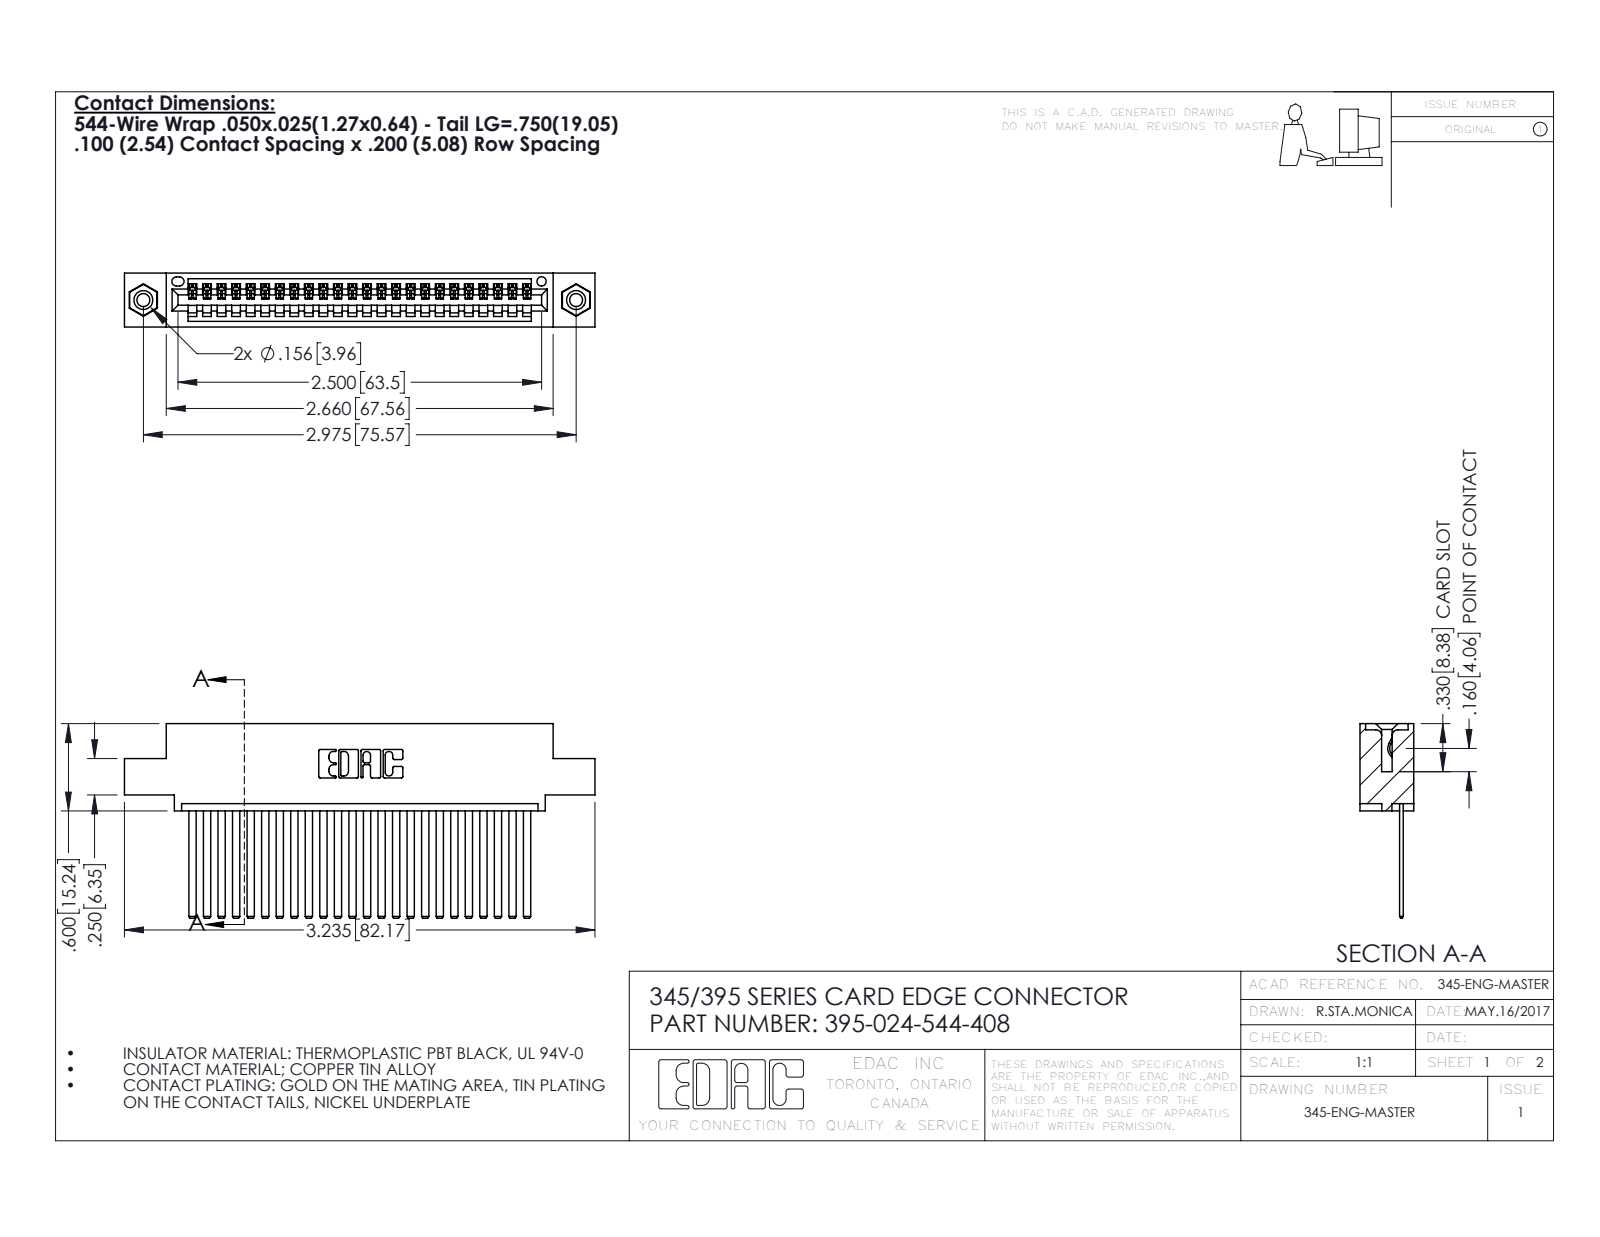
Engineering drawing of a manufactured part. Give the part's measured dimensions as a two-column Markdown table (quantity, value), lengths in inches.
| quantity | value |
| --- | --- |
| part name | 345 Part_0.110 Offset - 0.156 Dia-TI; 345-250-001_345-250-003-102; 395-024-544-408; 345-292-001_345-293-144 |
| STEP written by | SolidWorks 2016 (CONFIG_CONTROL_DESIGN) |
| units | inches |
| bodies | 27 solids, 1438 faces (980 planar, 442 cylindrical, 16 other) |
| overall size | 3.235 × 1.337 × 0.37 |
| volume | 0.479 in³ |
| surface area | 17.25 in² |
| round holes (diameter × count) | 0.089 × 2, 0.125 × 2, 0.156 × 2, 0.064 × 1 |
| round bosses / shafts (diameter × count) | 0.155 × 2 |
| partial cylindrical surfaces (radius × count) | 0.006 × 48, 0.01 × 22, 0.007 × 6, 0.031 × 6, 0.026 × 3, 0.031 × 2, 0.04 × 2, 0.014 × 1 |
| main face-to-face distances | 0.072, 0.298, 0.098, 0.025, 0.272, 0.37, 0.2, 0.225, 0.149, 0.072 |
| hole center spacings | 0.27, 2.741, 2.975 |
